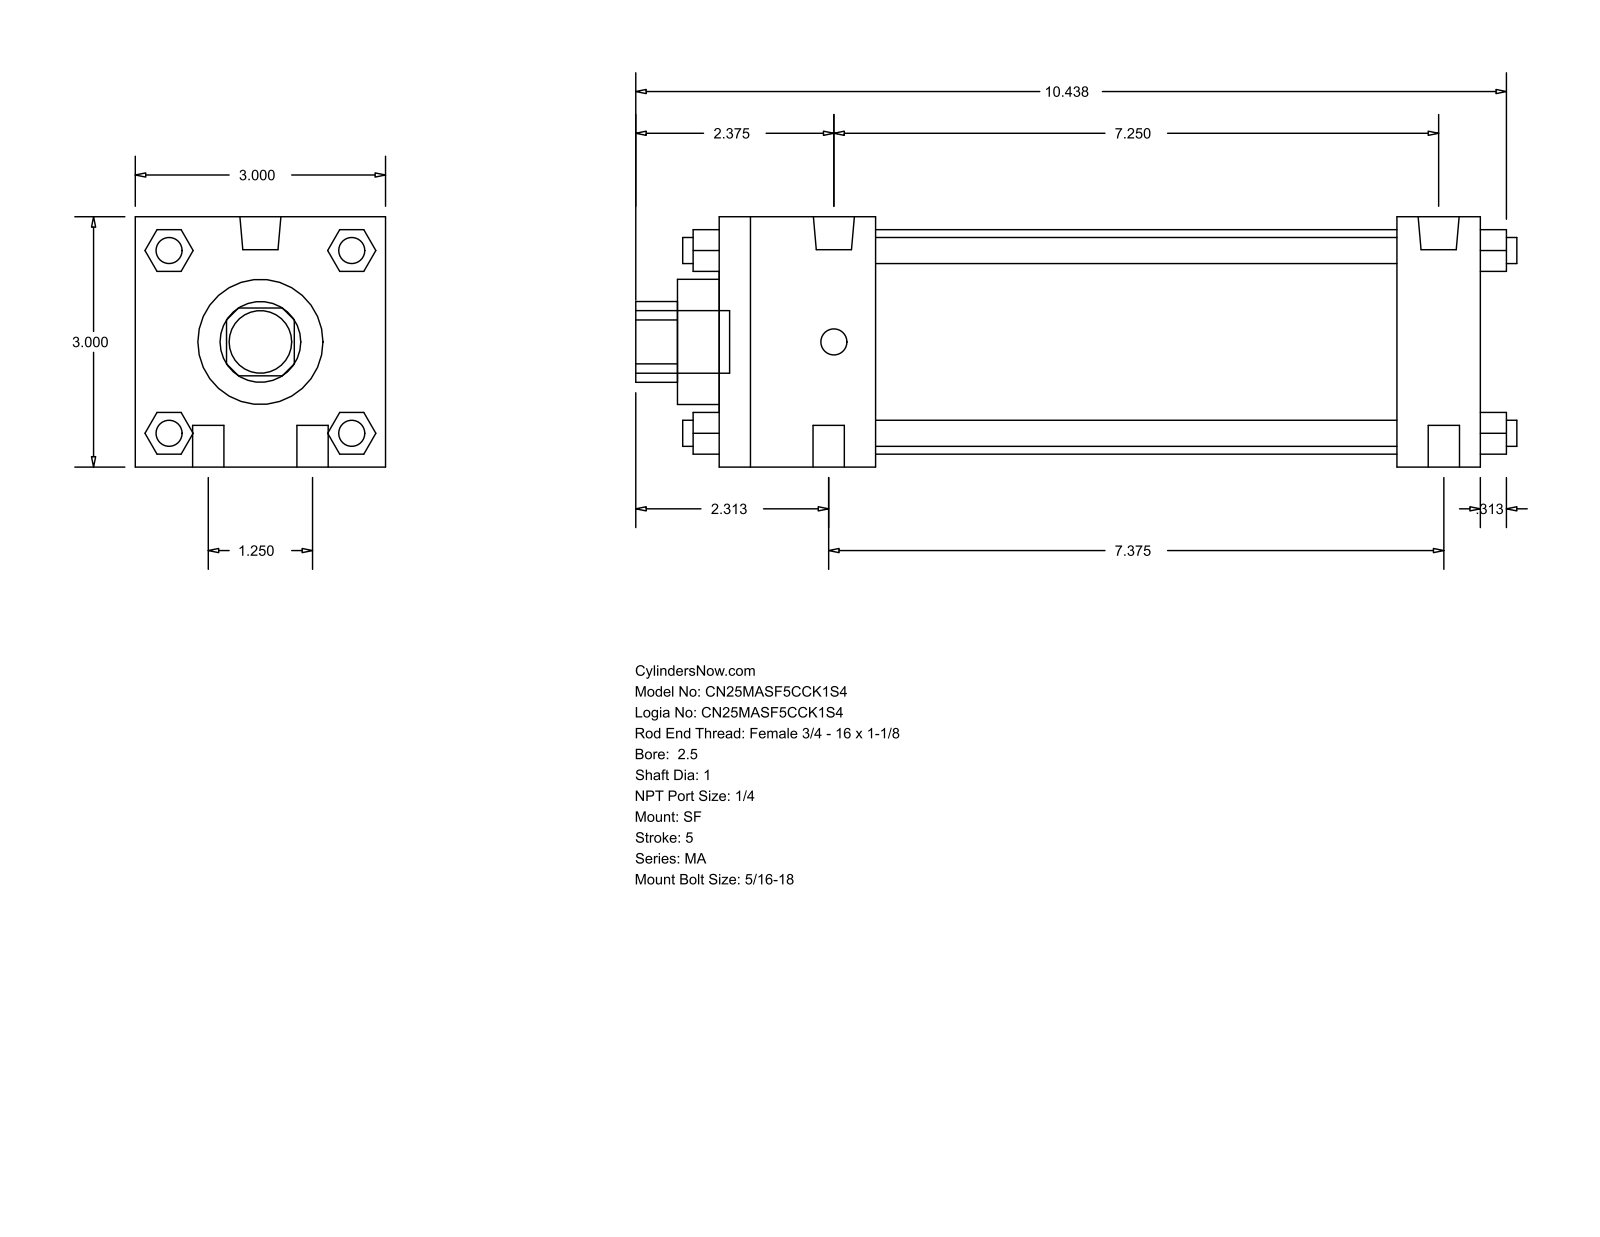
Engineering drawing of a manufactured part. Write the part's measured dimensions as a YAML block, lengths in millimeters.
part_name: "MA_SF__0250_1"
step_written_by: "GSSL Pune (CONFIG_CONTROL_DESIGN)"
units: millimeters
bodies: {solids: 0, faces: 124, planar: 94, cylindrical: 30, other: 0}
overall_size: [268.29, 76.2, 76.2]
round_holes:
  - {diameter: 25.4, count: 1}
  - {diameter: 38.1, count: 1}
  - {diameter: 68.33, count: 1}
round_bosses_or_shafts:
  - {diameter: 7.94, count: 6}
  - {diameter: 9.53, count: 4}
  - {diameter: 12.49, count: 2}
  - {diameter: 19.05, count: 1}
partial_cylinders:
  - {radius: 12.29, count: 1}
face_to_face_distances: [76.2, 231.78, 12.7, 25.4, 206.38, 47.63, 158.75, 184.15, 27.81, 48.17]
